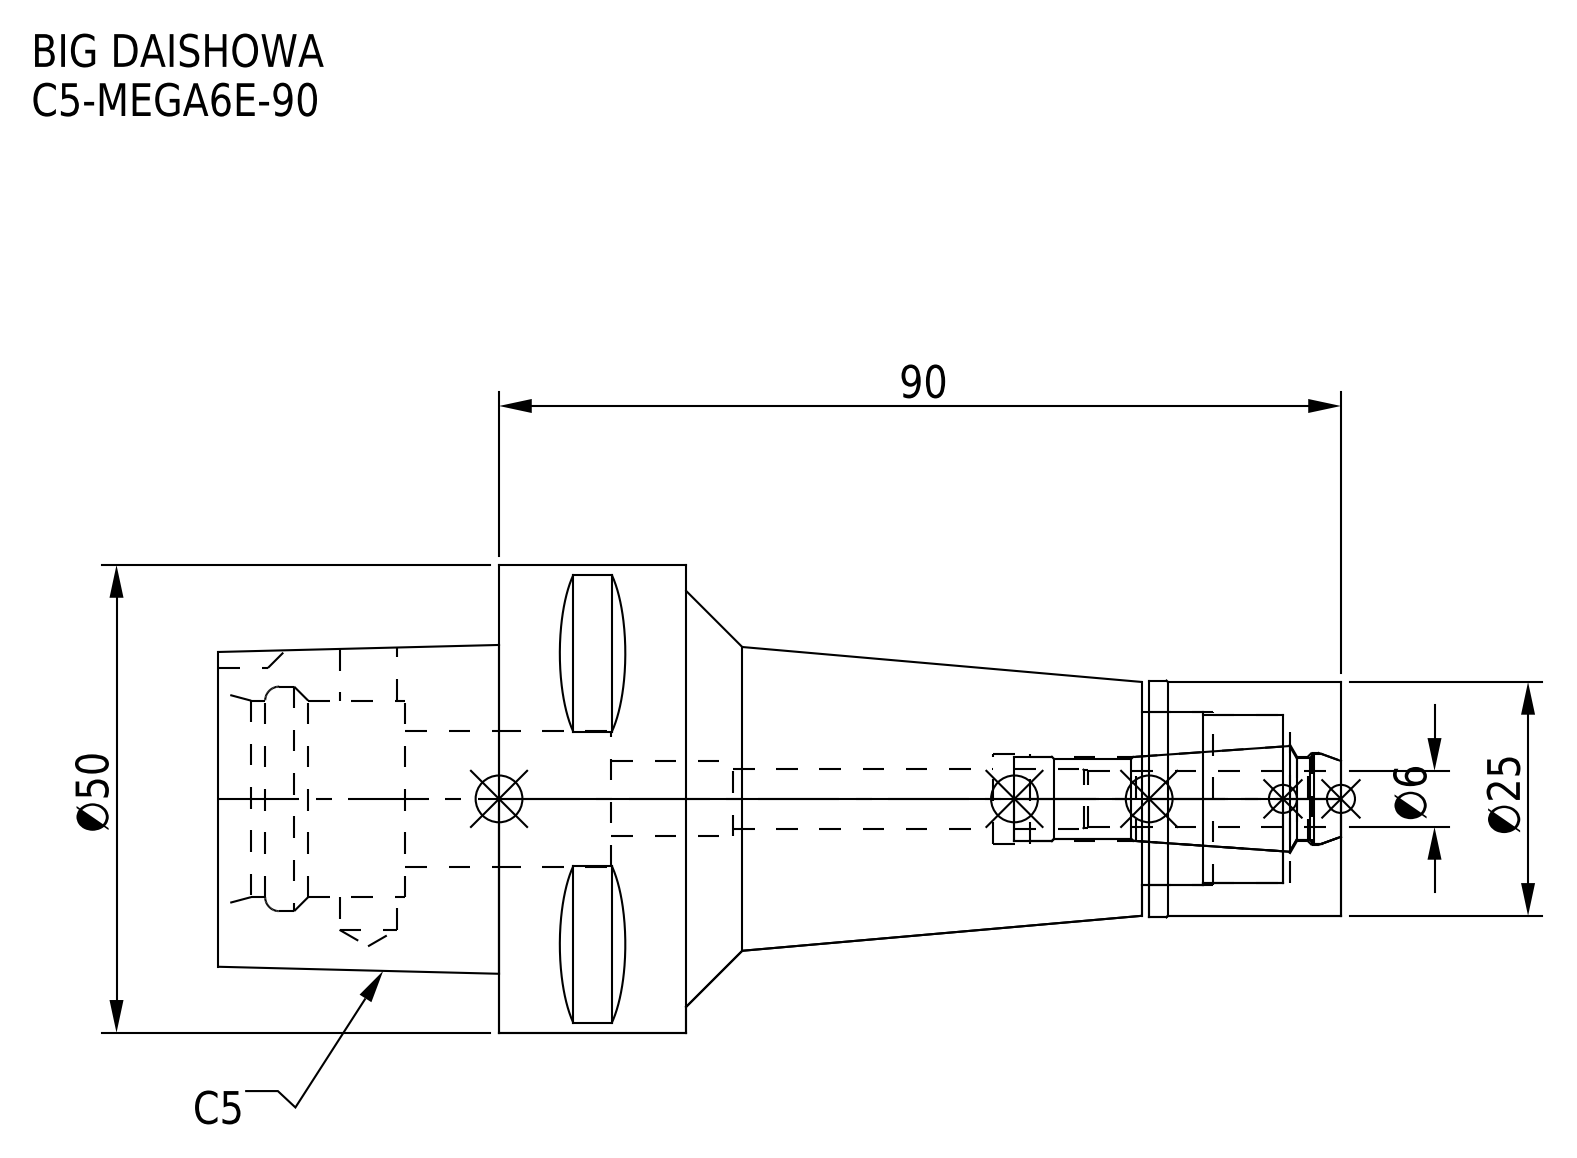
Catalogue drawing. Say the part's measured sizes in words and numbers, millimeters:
The part is named "C5-MEGA6E-90-060.stp; C5-MEGA6E-90; MEN6_1.stp; DXF_TEMP_ASSY_ASM_4_ASM.stp (+3 more)". Its 3-D file was written by "SolidWorks 2019 (CONFIG_CONTROL_DESIGN)". It is 2 solids with 100 faces: 37 planar, 39 cylindrical and 24 other. Overall it measures 120 by 50 by 50 millimeters. Its volume is 95 283 cubic millimeters and its surface area 22 919 square millimeters. Round holes: 1 of diameter 6.1, 1 of diameter 6.4, 1 of diameter 8, 1 of diameter 9, 1 of diameter 9.6, 1 of diameter 9.9, 1 of diameter 14.5, 1 of diameter 18, 1 of diameter 18.5, 1 of diameter 21, 1 of diameter 24. Round bosses or shafts: 1 of diameter 50, 1 of diameter 25.3, 1 of diameter 25. Partial cylindrical surfaces (rounded edges, fillets, slot ends): 1 of radius 4. The main face-to-face distances are 20, 30, 90, 70, 120, 50, 20.5, 49.5, 69.5, 99.5.
